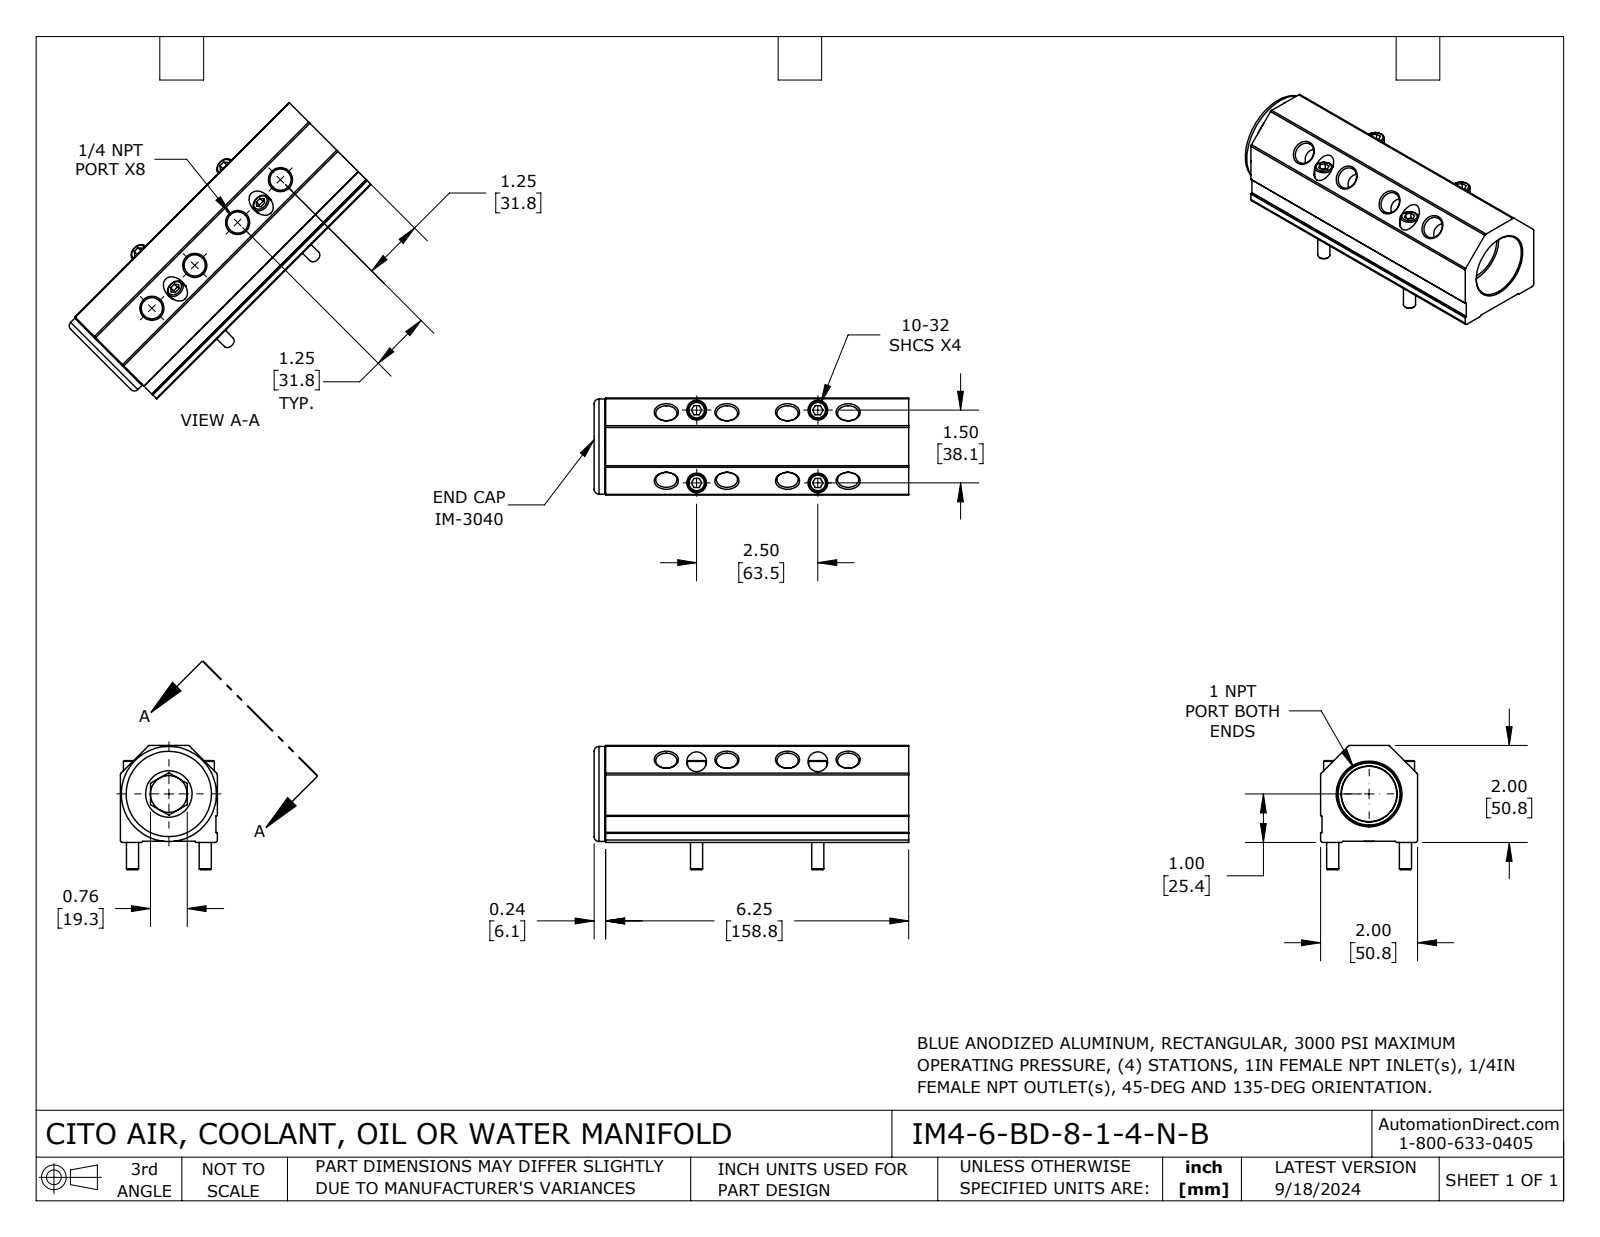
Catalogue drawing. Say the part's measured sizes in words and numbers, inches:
The part is named "IM4-6-BD-8-1-4-N-B". Its 3-D file was written by "SolidWorks 2023 (CONFIG_CONTROL_DESIGN)". It is 6 solids with 213 faces: 81 planar, 74 cylindrical and 58 other. Overall it measures 6.49 by 2.56 by 2 inches. Its volume is 16.22 cubic inches and its surface area 101.9 square inches. Round holes: 8 of diameter 0.437, 4 of diameter 0.266, 4 of diameter 0.406, 1 of diameter 0.758, 1 of diameter 1.156, 1 of diameter 1.637. Round bosses or shafts: 4 of diameter 0.375, 4 of diameter 0.25, 1 of diameter 1.96, 1 of diameter 1.359, 1 of diameter 1.293, 1 of diameter 1.14. Partial cylindrical surfaces (rounded edges, fillets, slot ends): 8 of radius 0.05, 4 of radius 0.01. The main face-to-face distances are 2, 1.975, 0.025, 6.25, 0.028, 1.972, 0.24, 6.49, 0.764, 0.524. The hole center spacings are 1.25, 2.5, 1.5, 2.915, 3.75.
